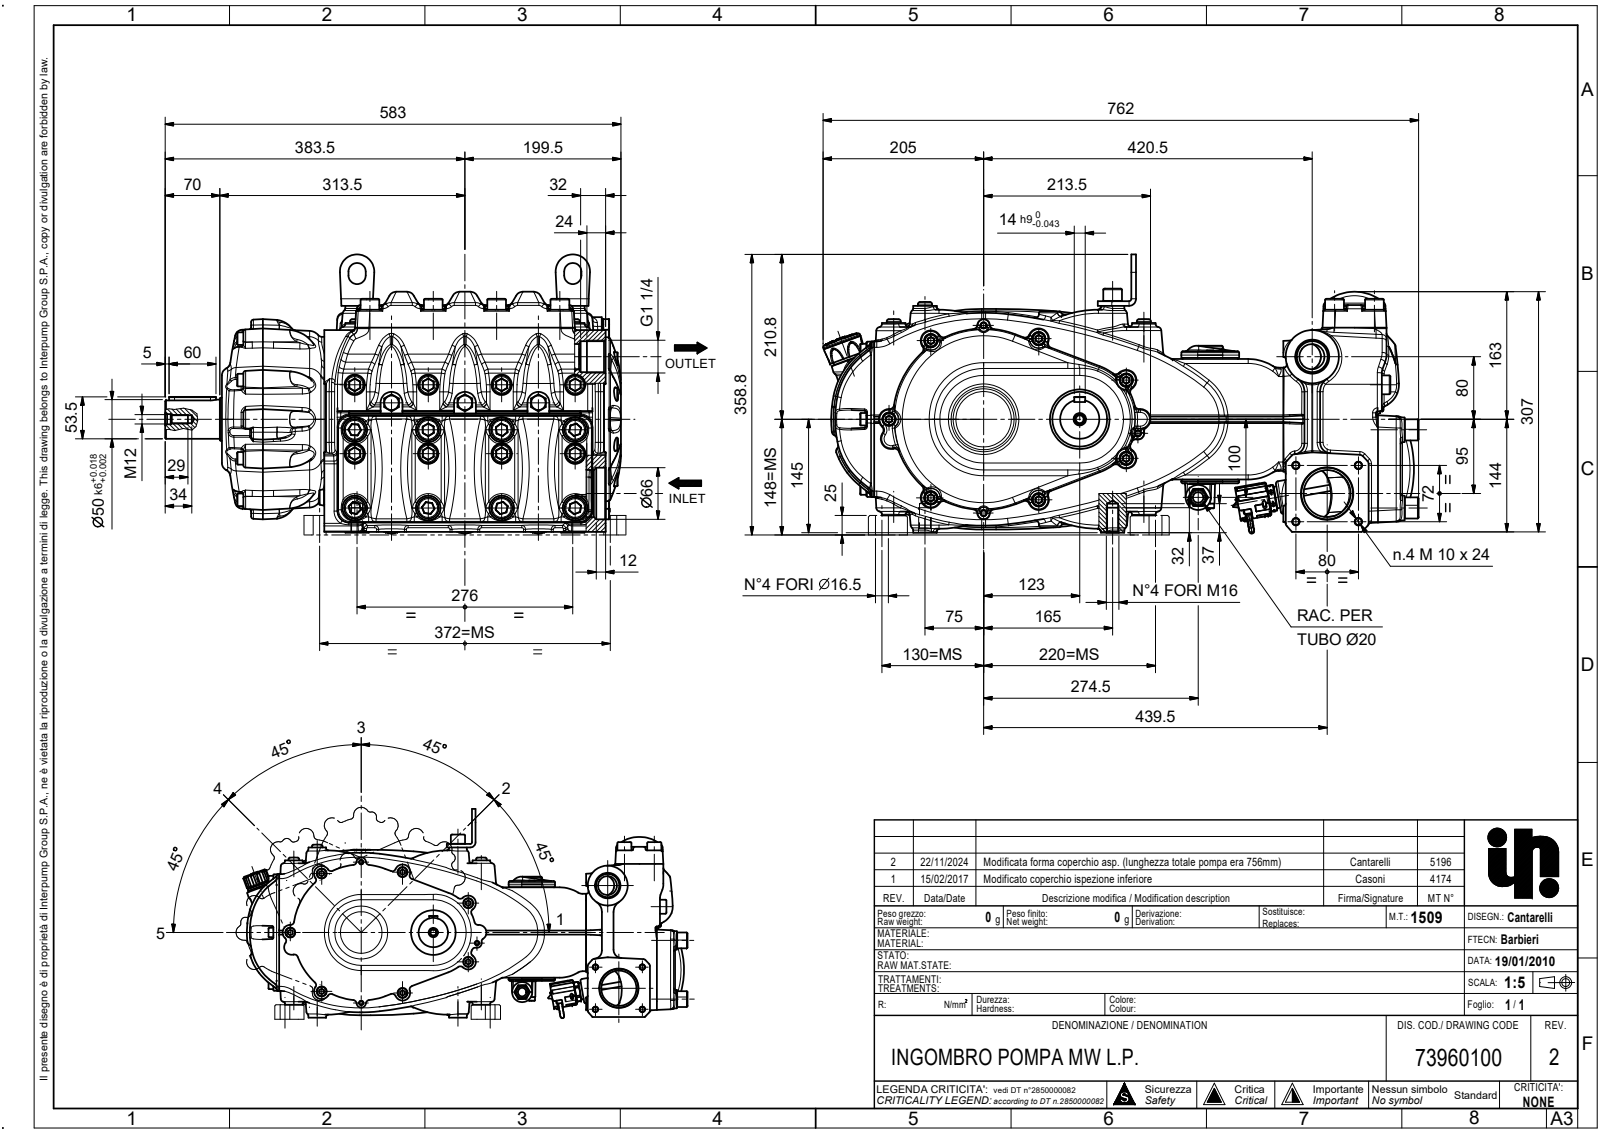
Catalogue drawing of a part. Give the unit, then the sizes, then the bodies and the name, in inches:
Units: inches
Overall size (bounding box): 29.757 × 22.952 × 14.052
Round holes (diameter × count): ⌀0.551 ×33, ⌀0.669 ×31, ⌀0.335 ×23, ⌀0.984 ×20, ⌀0.138 ×12, ⌀0.315 ×11, ⌀0.65 ×10, ⌀0.197 ×8, ⌀0.433 ×8, ⌀0.846 ×8, ⌀0.413 ×7, ⌀0.787 ×7
Round bosses / shafts (diameter × count): ⌀0.63 ×47, ⌀0.394 ×29, ⌀0.945 ×26, ⌀1.063 ×11, ⌀0.709 ×8, ⌀0.825 ×7, ⌀0.315 ×7, ⌀0.661 ×6
Partial cylindrical surfaces — rounded edges, fillets, slot ends (radius × count): R0.02 ×1031, R0.079 ×203, R0.012 ×120, R0.008 ×86, R0.197 ×86, R0.006 ×62, R0.059 ×62, R0.157 ×58
Main face-to-face distances: 25.374, 4.764, 20.61, 0.02, 13.799, 13.78, 17.067, 3.287, 13.372, 1.575
Hole centre spacings: 3.701, 7.402, 3.465, 1.063, 1.884, 6.111, 4.764, 2.638
Volume: 3 788 in³ · Surface area: 4 444 in²
Bodies: 203 solids, 14880 faces (3606 planar, 3796 cylindrical, 7478 other)
STEP written by: THINKDESIGN (AUTOMOTIVE_DESIGN)
